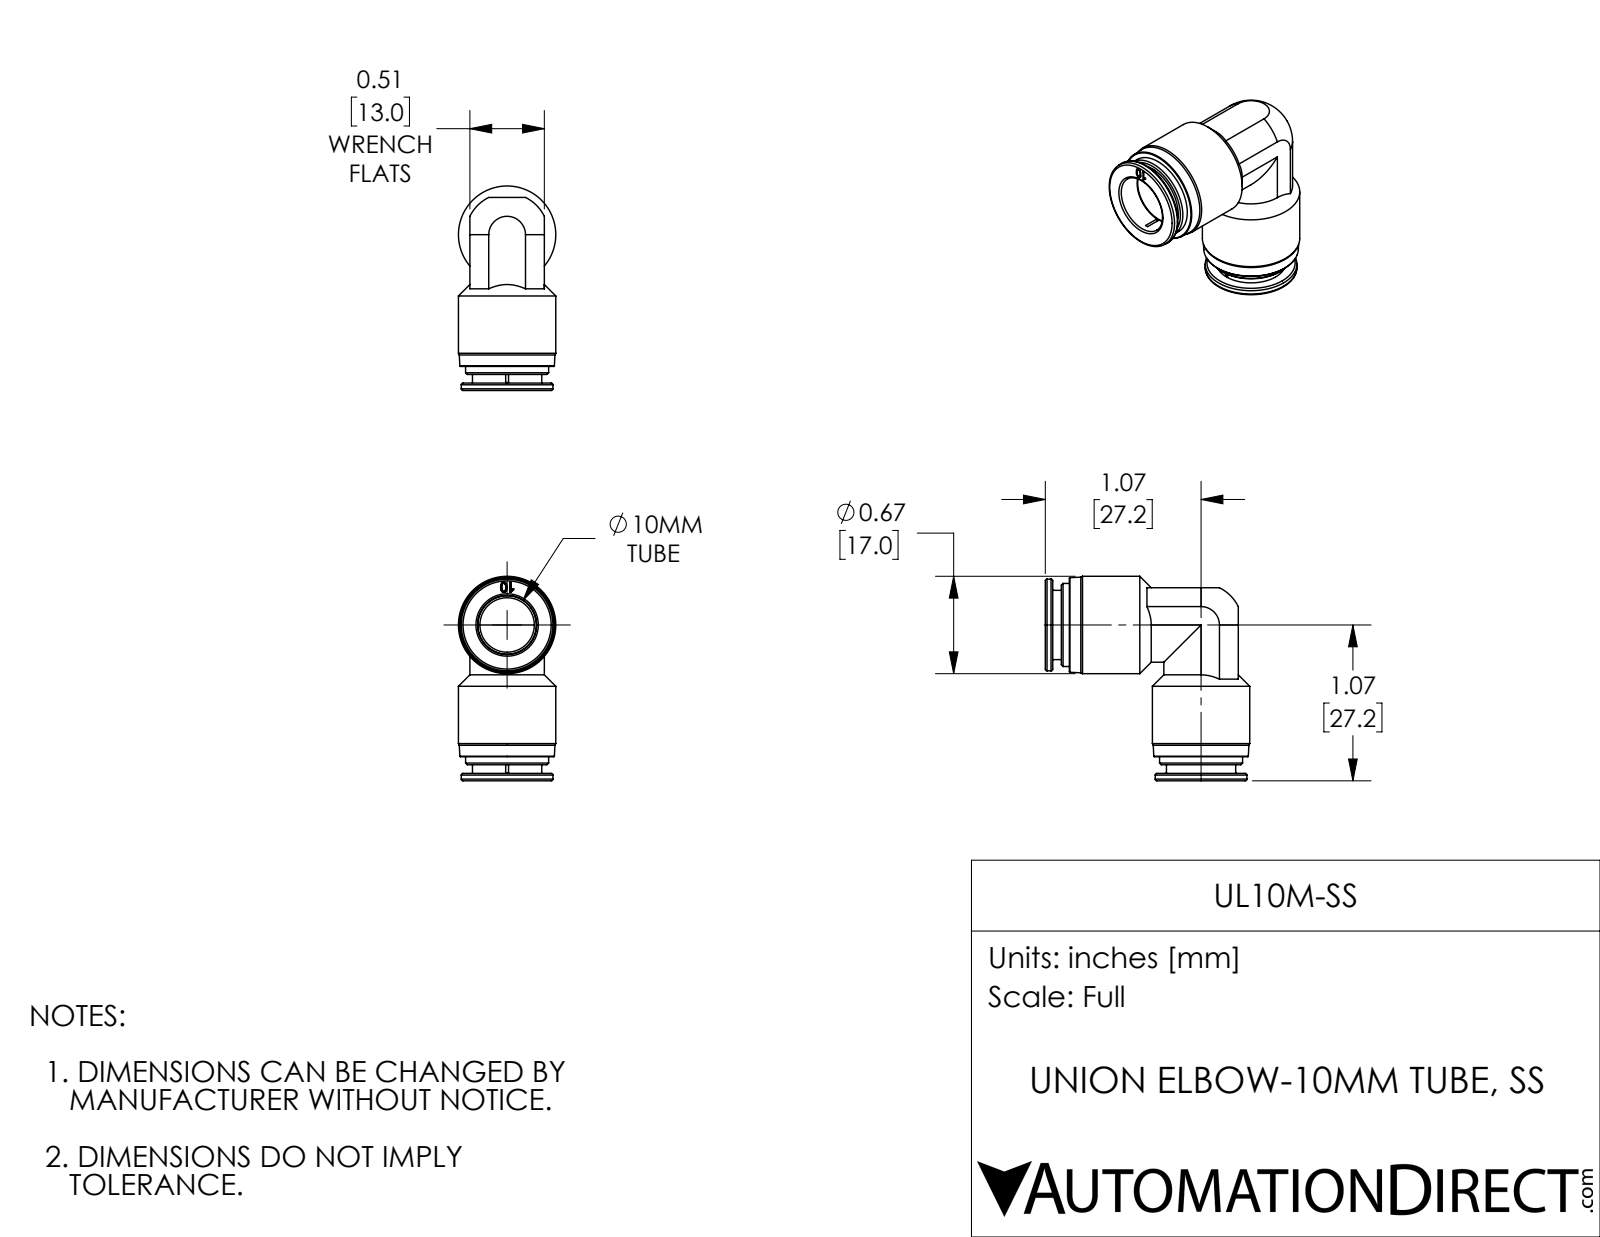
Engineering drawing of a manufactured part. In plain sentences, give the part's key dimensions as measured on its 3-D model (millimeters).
The part is named "UL10M-SS". Its 3-D file was written by "SolidWorks 2017 (AUTOMOTIVE_DESIGN)". It is 1 solid with 151 faces: 44 planar, 35 cylindrical and 72 other. Overall it measures 35.7 by 35.7 by 17 millimeters. Its volume is 5 750 cubic millimeters and its surface area 5 170 square millimeters. Round holes: 2 of diameter 9.5, 2 of diameter 10.2, 2 of diameter 10.3. Round bosses or shafts: 2 of diameter 17, 2 of diameter 16, 2 of diameter 14.5, 2 of diameter 12.1. Partial cylindrical surfaces (rounded edges, fillets, slot ends): 2 of radius 6.5. The main face-to-face distances are 33.7, 1.3, 32.4, 4.2, 2.9, 29.5, 13, 1.4, 2.8, 1.5.
